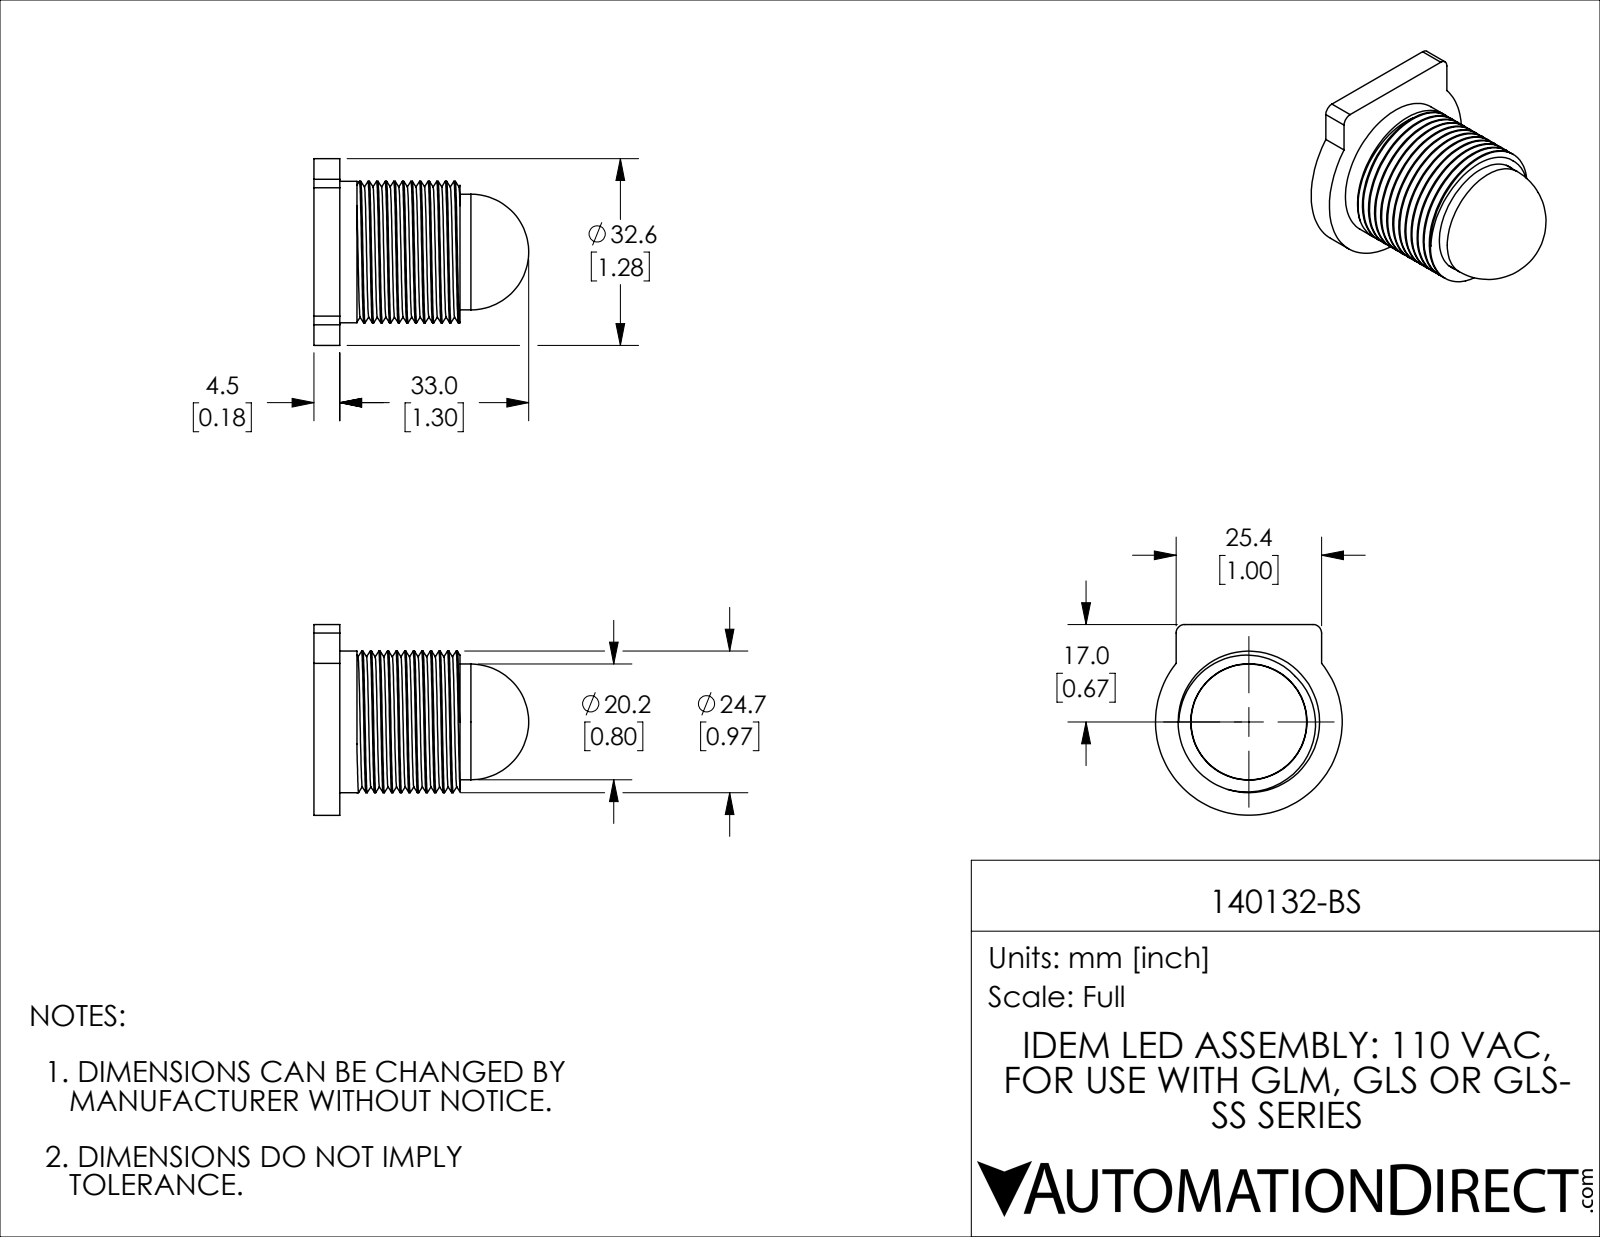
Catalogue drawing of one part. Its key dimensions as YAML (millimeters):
part_name: "140132-BS"
step_written_by: "SolidWorks 2021 (CONFIG_CONTROL_DESIGN)"
units: millimeters
bodies: {solids: 2, faces: 69, planar: 20, cylindrical: 45, other: 4}
overall_size: [37.5, 33.3, 32.6]
volume: 15100
surface_area: 7258
round_holes:
  - {diameter: 16.5, count: 1}
  - {diameter: 19, count: 1}
  - {diameter: 20.3, count: 1}
round_bosses_or_shafts:
  - {diameter: 0.5, count: 3}
  - {diameter: 24.7, count: 1}
  - {diameter: 20.2, count: 1}
partial_cylinders:
  - {radius: 1.5, count: 2}
  - {radius: 16.3, count: 1}
face_to_face_distances: [4.5, 15, 10.5, 19.5, 13, 2, 2.5, 17.5, 8, 6]
